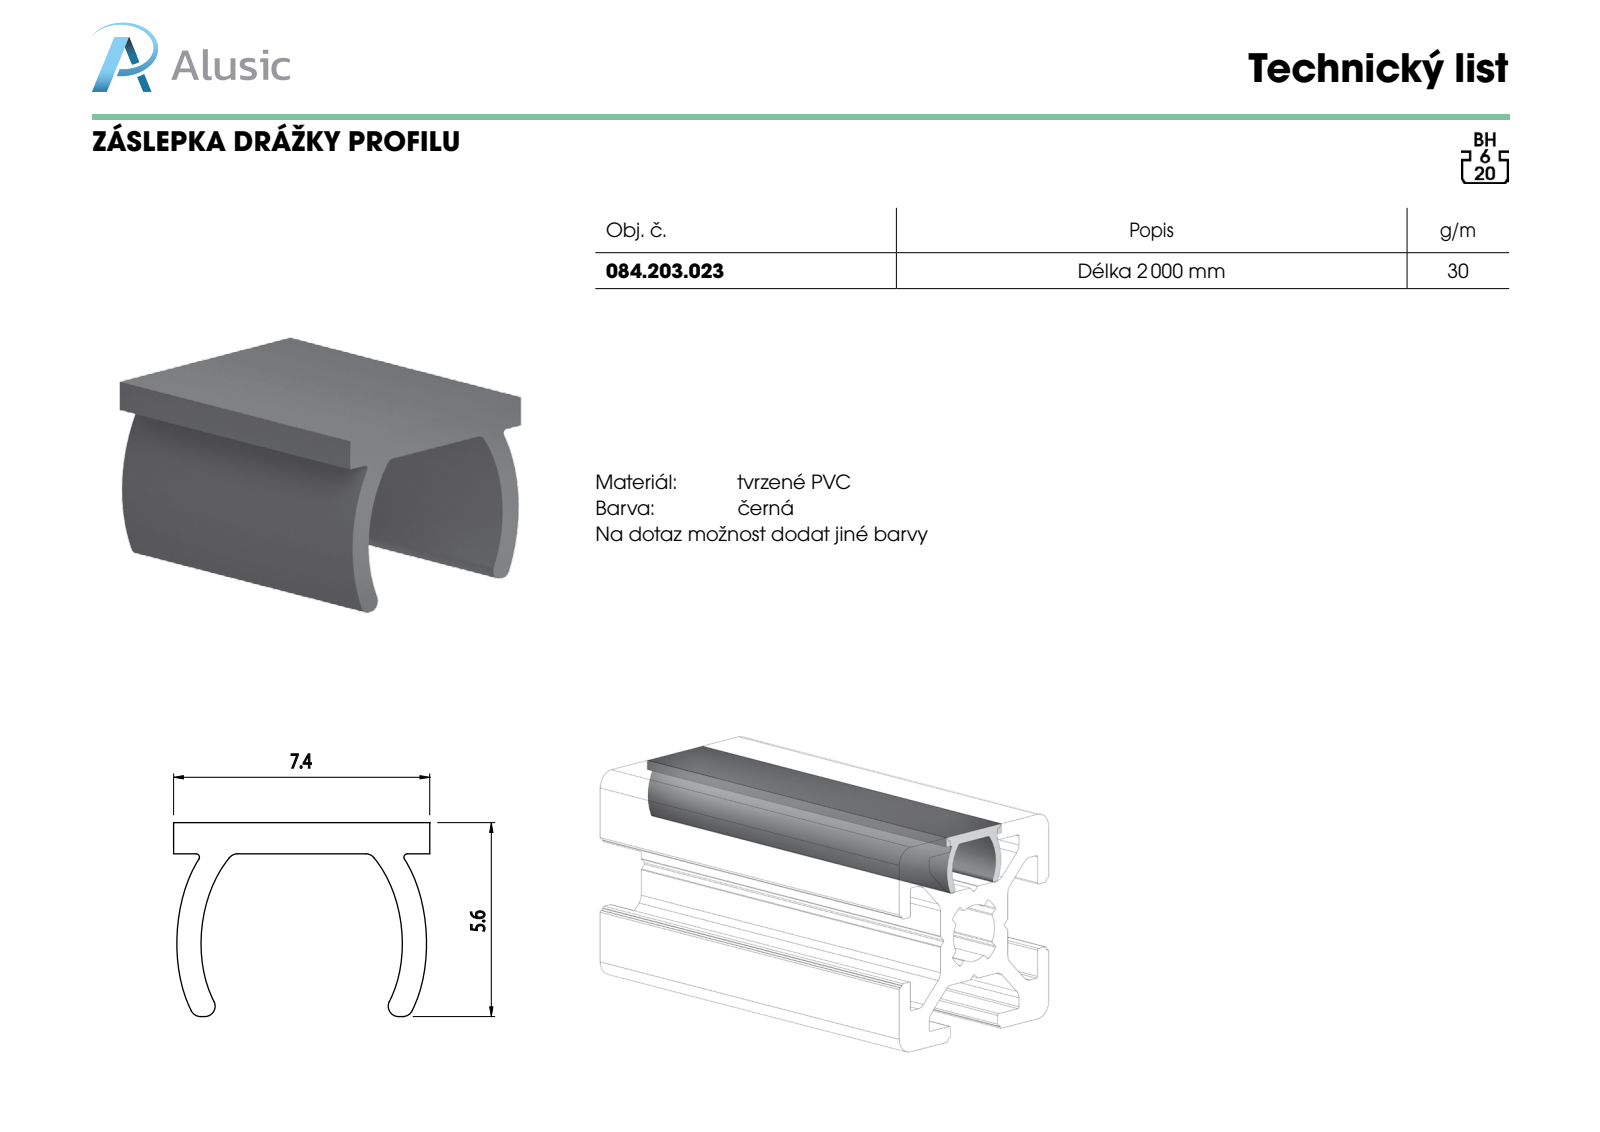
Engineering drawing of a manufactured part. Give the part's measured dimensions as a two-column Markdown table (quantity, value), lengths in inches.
| quantity | value |
| --- | --- |
| part name | 084.203.023 |
| STEP written by | SolidWorks 2012 (CONFIG_CONTROL_DESIGN) |
| units | inches |
| bodies | 1 solid, 22 faces (10 planar, 12 cylindrical, 0 other) |
| overall size | 3.937 × 0.291 × 0.22 |
| volume | 0.083 in³ |
| surface area | 5.492 in² |
| partial cylindrical surfaces (radius × count) | 0.012 × 6, 0.004 × 2, 0.161 × 2, 0.192 × 2 |
| main face-to-face distances | 0.035, 0.291, 0.185, 0.22, 3.937 |
